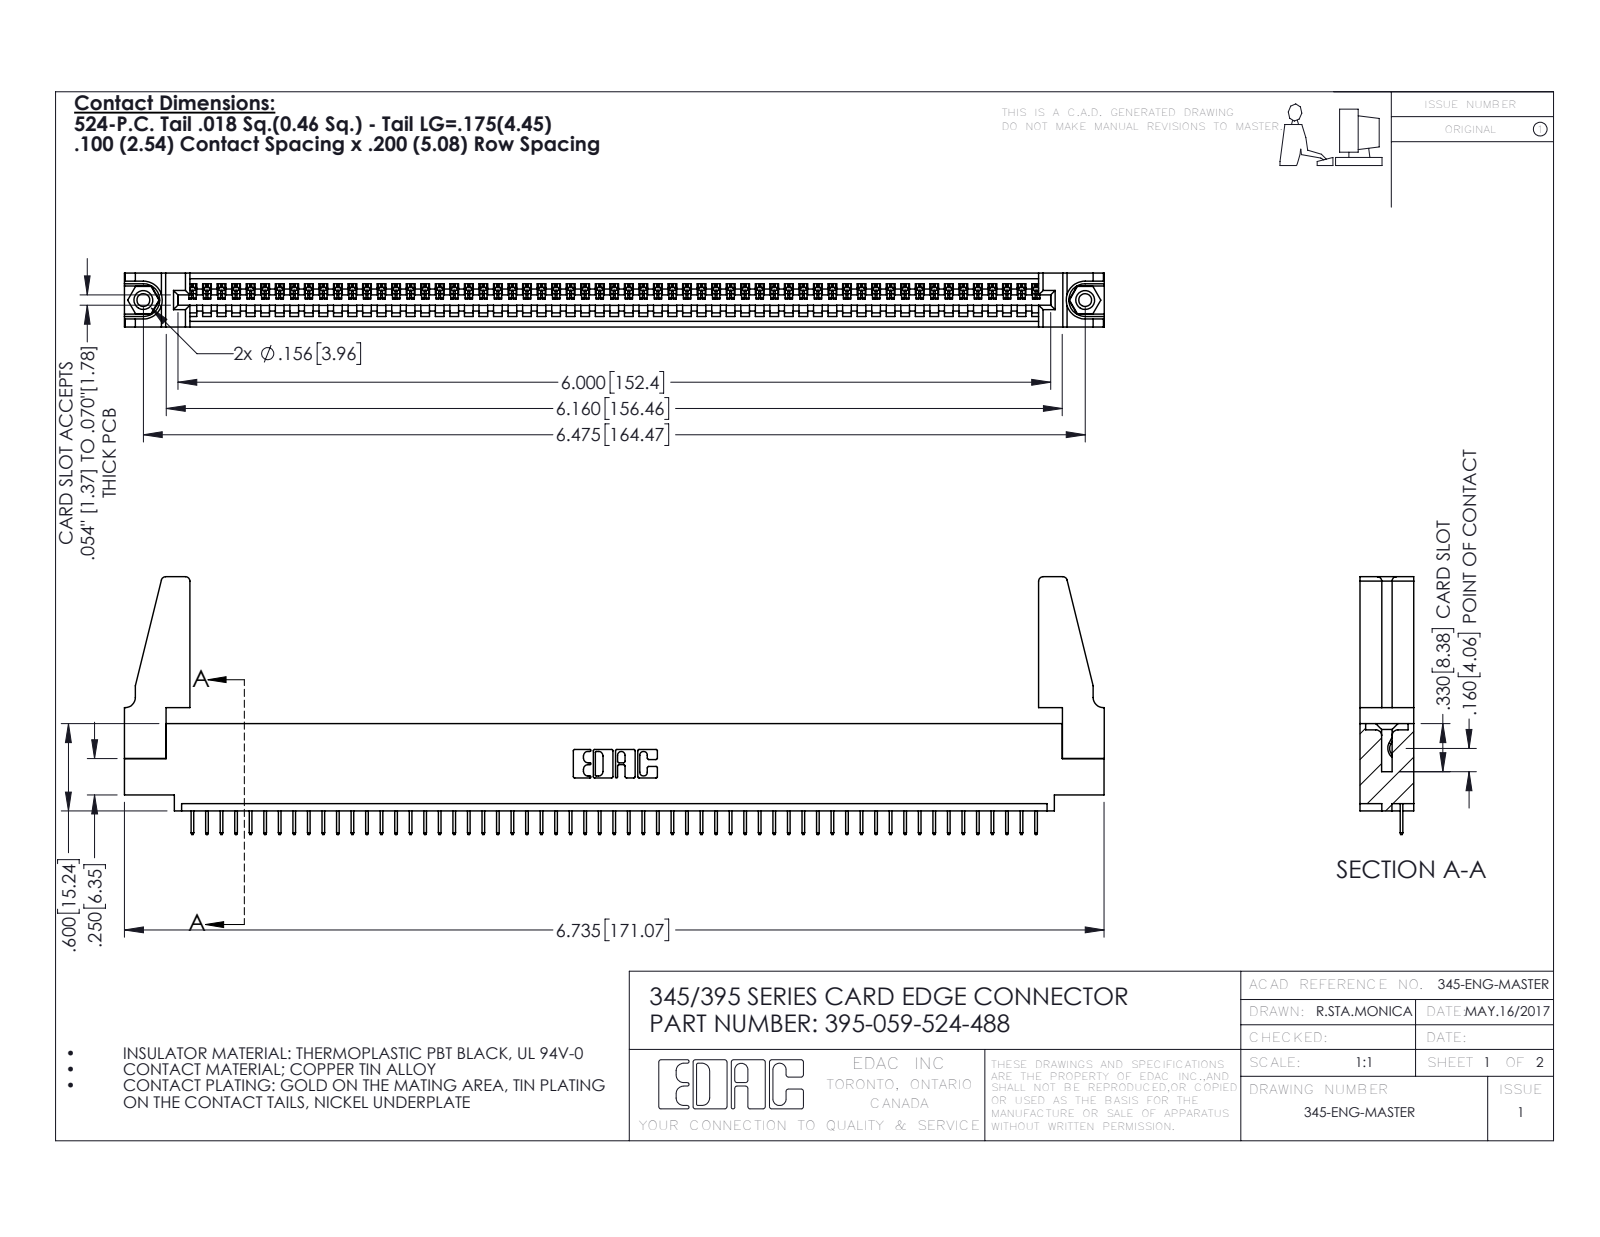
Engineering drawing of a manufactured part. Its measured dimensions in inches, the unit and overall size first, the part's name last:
Units: inches
Overall size (bounding box): 6.736 × 1.772 × 0.37
Round holes (diameter × count): ⌀0.089 ×2, ⌀0.125 ×2, ⌀0.156 ×2, ⌀0.064 ×1
Round bosses / shafts (diameter × count): ⌀0.155 ×2
Partial cylindrical surfaces — rounded edges, fillets, slot ends (radius × count): R0.006 ×118, R0.01 ×22, R0.03 ×8, R0.007 ×6, R0.031 ×6, R0.026 ×3, R0.031 ×2, R0.04 ×2
Main face-to-face distances: 0.072, 0.298, 0.37, 0.2, 0.098, 0.272, 0.025, 0.225, 0.072, 0.149
Hole centre spacings: 0.27, 6.239, 6.475
Volume: 1.18 in³ · Surface area: 37.31 in²
Bodies: 64 solids, 3912 faces (2870 planar, 1026 cylindrical, 16 other)
Part name (STEP PRODUCT): 345-250-001_345-250-001-102; 395-059-524-488; 345-220-078_345-220-088; 345-292-001_345-293-124 (+1 more)
STEP written by: SolidWorks 2016 (CONFIG_CONTROL_DESIGN)
